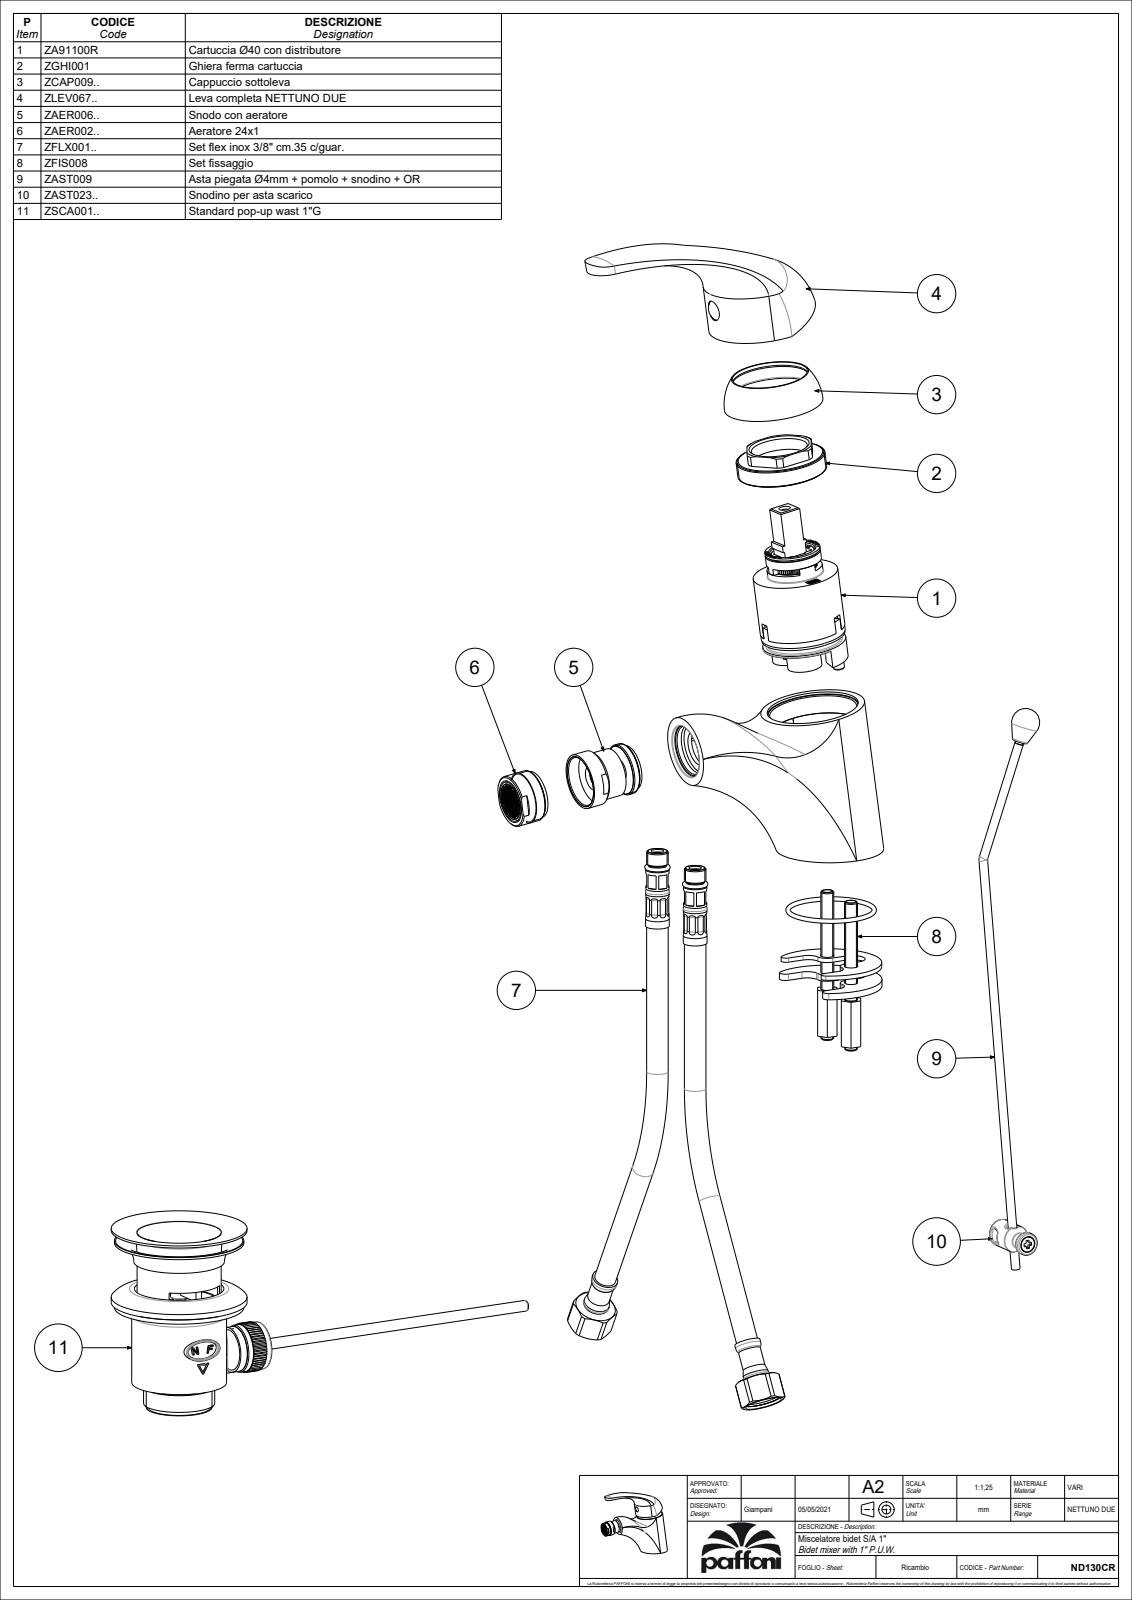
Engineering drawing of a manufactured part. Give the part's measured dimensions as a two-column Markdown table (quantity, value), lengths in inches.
| quantity | value |
| --- | --- |
| part name | ND135CR |
| STEP written by | CREO PARAMETRIC BY PTC INC, 2020044 (CONFIG_CONTROL_DESIGN) |
| units | inches |
| bodies | 4 solids, 2758 faces (2024 planar, 403 cylindrical, 331 other) |
| overall size | 5.681 × 4.722 × 2.008 |
| volume | 9.972 in³ |
| surface area | 143.7 in² |
| round holes (diameter × count) | 0.315 × 5, 0.433 × 3, 0.13 × 2, 0.181 × 2, 0.197 × 2, 0.276 × 2, 0.354 × 2, 0.472 × 2, 0.63 × 2, 0.827 × 2, 0.157 × 1, 0.236 × 1 |
| round bosses / shafts (diameter × count) | 0.394 × 3, 1.016 × 2, 0.945 × 2, 0.626 × 2, 0.37 × 2, 0.323 × 2, 0.315 × 2, 1.555 × 1 |
| partial cylindrical surfaces (radius × count) | 0.02 × 52, 0.008 × 24, 0.079 × 10, 0.012 × 8, 0.118 × 8, 0.059 × 4, 0.295 × 4, 0.039 × 2 |
| main face-to-face distances | 0.02, 0.177, 0.079, 0.138, 0.098, 0.039, 0.138, 0.059, 0.236, 0.394 |
| hole center spacings | 0.339, 0.338, 0.39, 0.551, 0.079, 0.389, 0.513, 0.557 |
